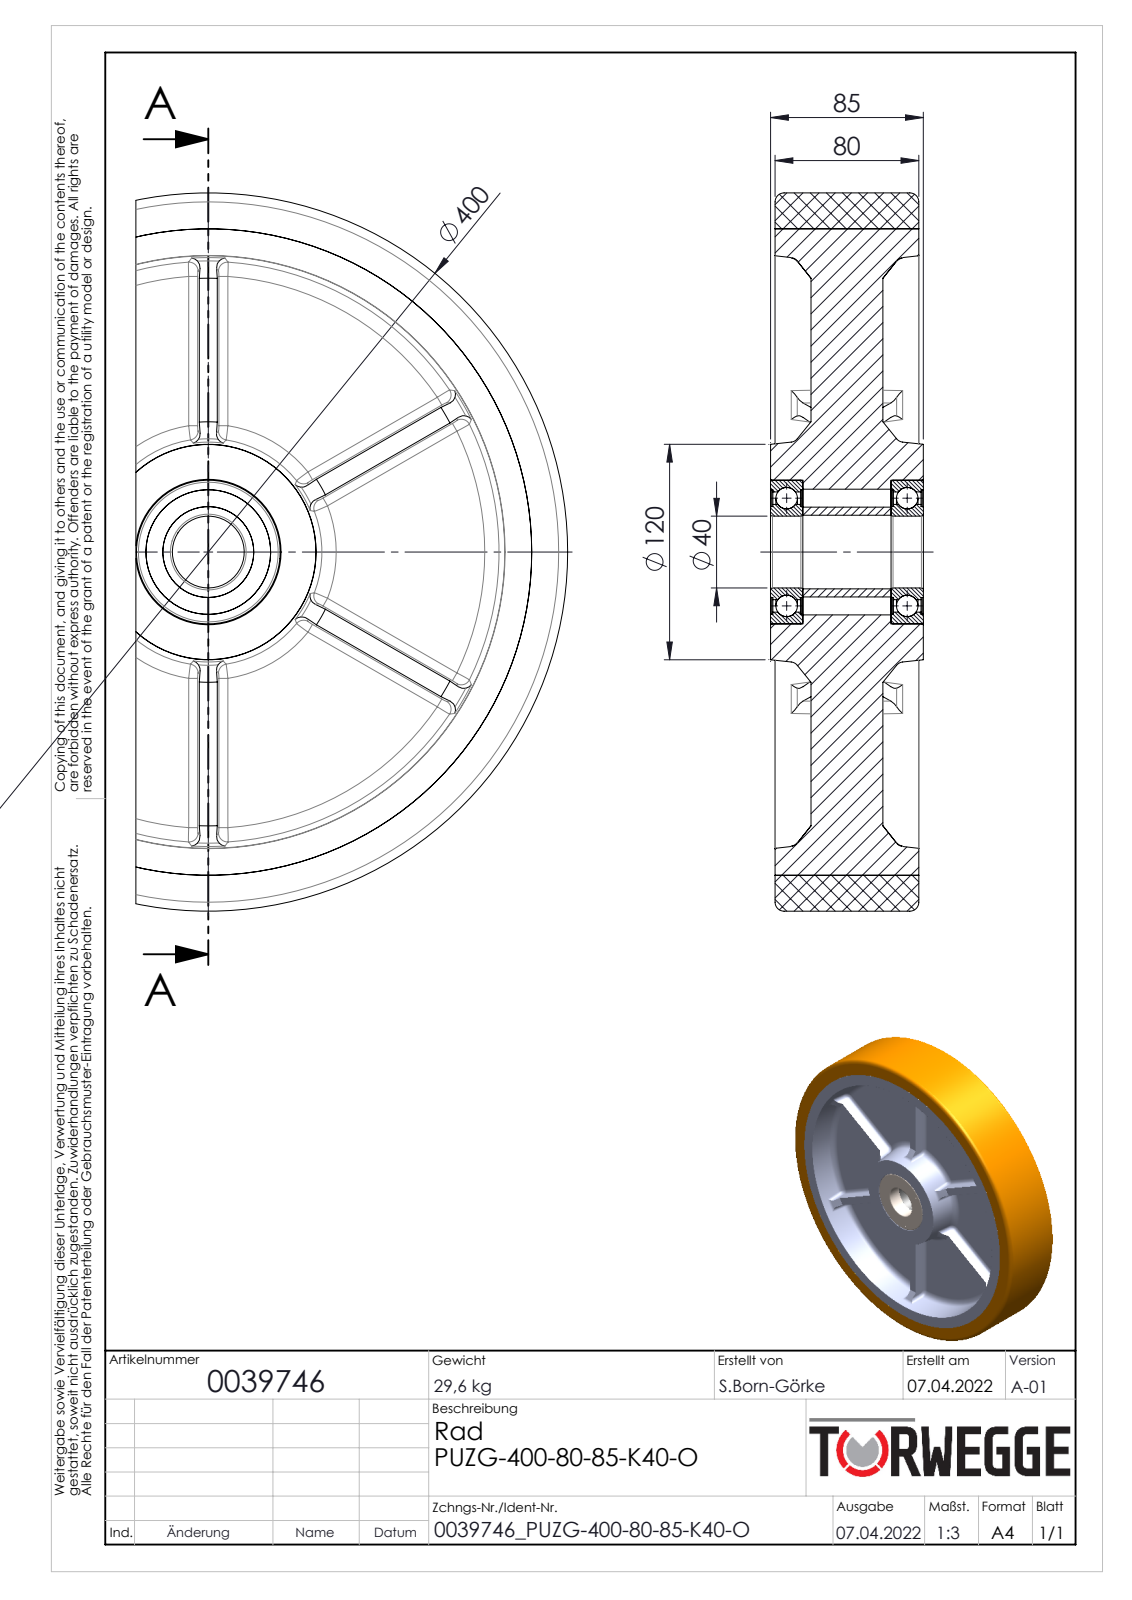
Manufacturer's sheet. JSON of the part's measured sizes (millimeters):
{"part_name": "0039746", "step_written_by": "SolidWorks 2020 (AUTOMOTIVE_DESIGN)", "units": "millimeters", "bodies": {"solids": 13, "faces": 410, "planar": 82, "cylindrical": 96, "other": 232}, "overall_size": [400, 400, 85.1], "volume_mm3": 5137000, "surface_area_mm2": 728363, "round_holes": [[40, 1], [41, 1], [50.6, 1], [66.96, 1], [69.4, 1], [70, 1], [80, 1], [360, 1]], "round_bosses_or_shafts": [[400, 1], [53.04, 1], [50, 1]], "partial_cylinders_radius": [[5, 16]], "face_to_face_distances": [35, 45, 10, 80, 2.5, 37.5, 47.5, 82.5, 13.44, 67.05]}
